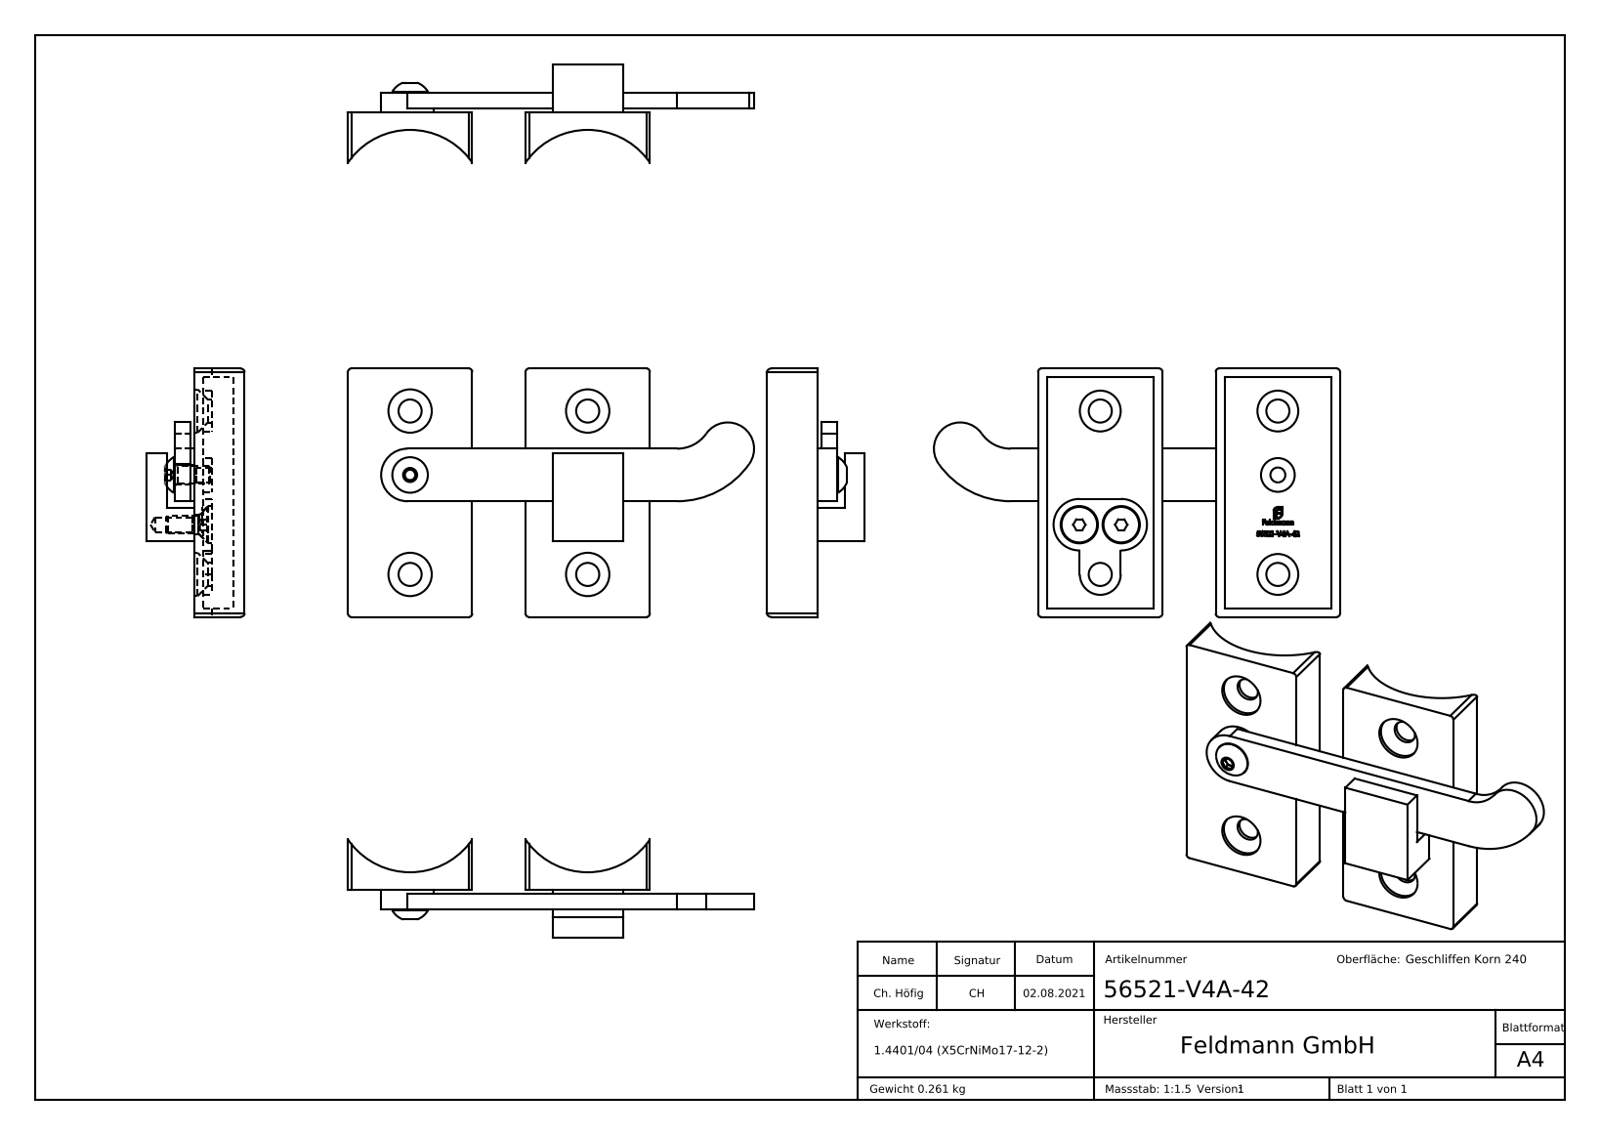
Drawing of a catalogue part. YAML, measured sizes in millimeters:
part_name: "5652X-V4A-XX Teil1; DIN 7991 Konfig; 56521-V4A-42; 5652X-V4A-XX Teil1_56521-V4A-XX Teil3 (+6 more)"
step_written_by: "SolidWorks 2018 (CONFIG_CONTROL_DESIGN)"
units: millimeters
bodies: {solids: 7, faces: 431, planar: 256, cylindrical: 43, other: 132}
overall_size: [114.34, 70, 27.53]
volume: 32580
surface_area: 26372
round_holes:
  - {diameter: 6.5, count: 4}
  - {diameter: 12.2, count: 4}
  - {diameter: 4.2, count: 3}
  - {diameter: 5.5, count: 3}
  - {diameter: 10.5, count: 2}
round_bosses_or_shafts:
  - {diameter: 11.5, count: 3}
  - {diameter: 10, count: 3}
  - {diameter: 5, count: 3}
  - {diameter: 14.8, count: 1}
  - {diameter: 9.5, count: 1}
partial_cylinders:
  - {radius: 1, count: 8}
  - {radius: 7.25, count: 2}
  - {radius: 21.2, count: 2}
  - {radius: 5.75, count: 1}
  - {radius: 7.4, count: 1}
  - {radius: 10.02, count: 1}
  - {radius: 24.8, count: 1}
face_to_face_distances: [2.5, 50, 32.5, 35, 5.5, 8, 4.5, 3.5, 1, 52.5]
hole_center_spacings: [15.19, 32.54, 46, 46.27, 50, 57.63, 67.94, 11.8]
